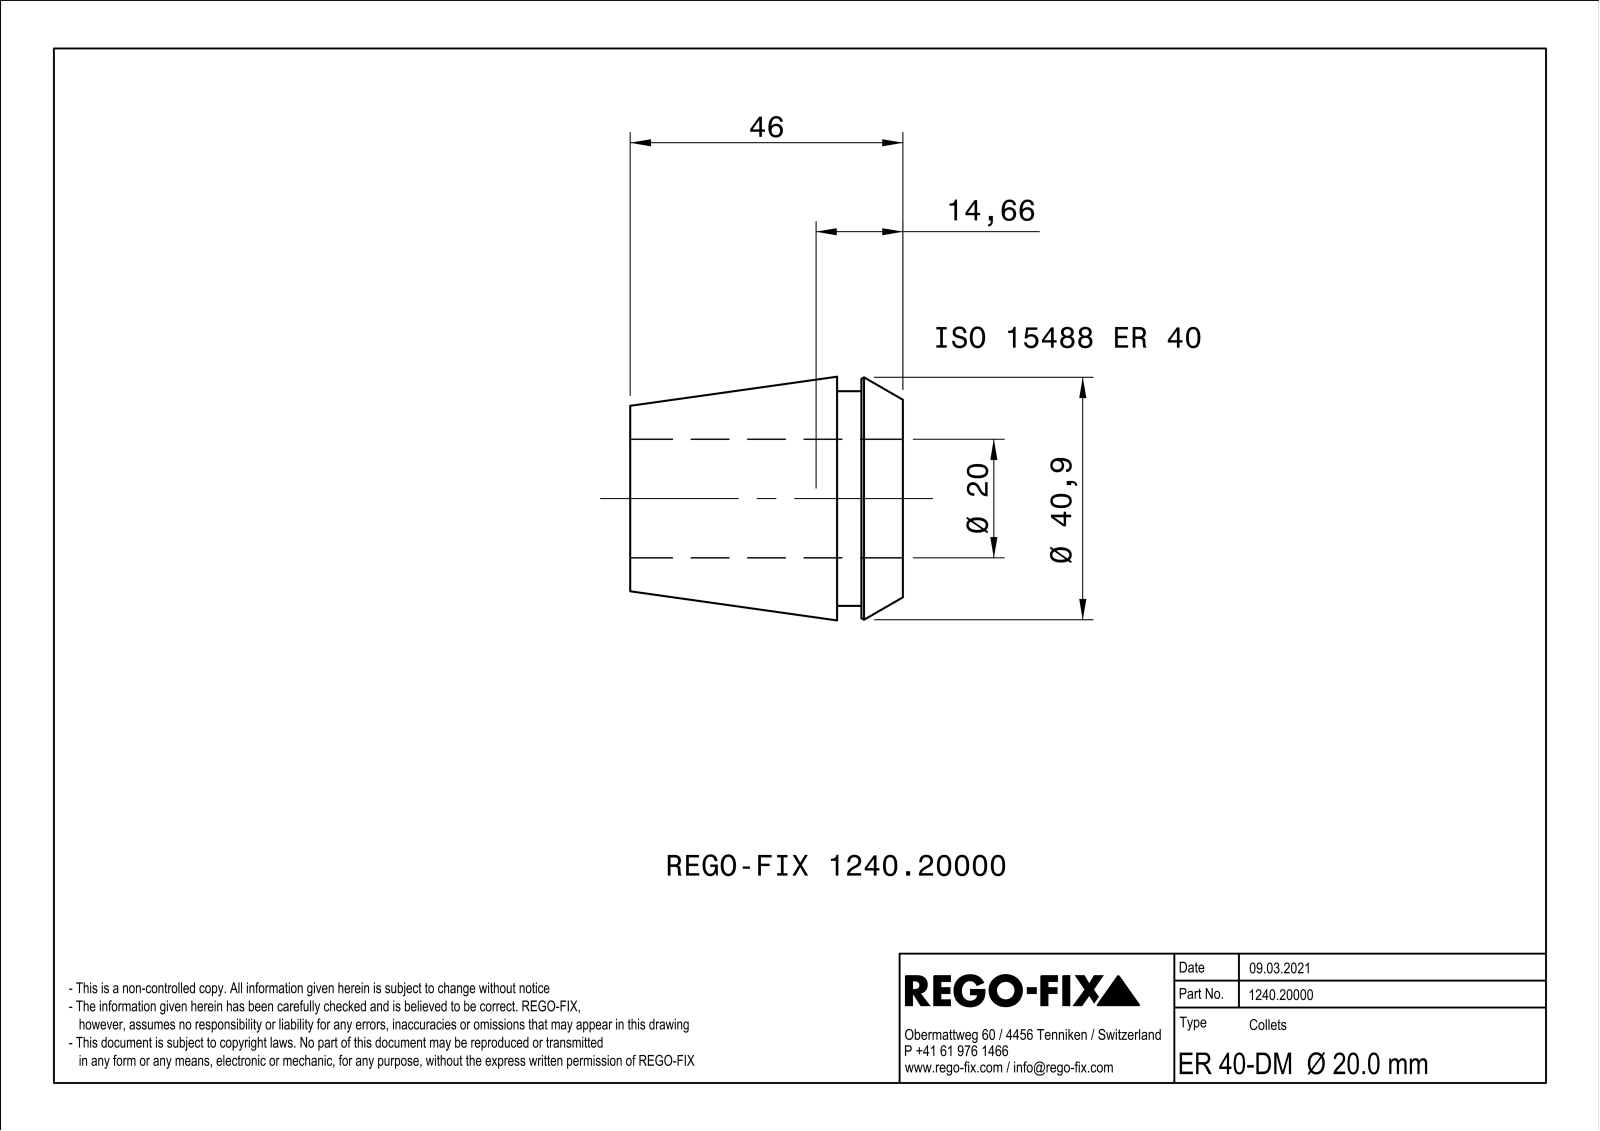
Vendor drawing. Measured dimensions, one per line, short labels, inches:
name: NOCUT
written by: SIEMENS PLM Software Solid Edge ST10 (AUTOMOTIVE_DESIGN)
unit: in
bodies: 1 solid, 154 faces (80 planar, 9 cylindrical, 65 other)
size: 1.811 × 1.614 × 1.614
volume: 1.761 in³; area: 27.49 in²
holes: 1× ⌀0.787
bosses: 1× ⌀1.425
face distances: 0.039, 1.811, 0.437, 1.374, 0.276, 0.161, 1.535, 0.669, 0.394, 0.232
